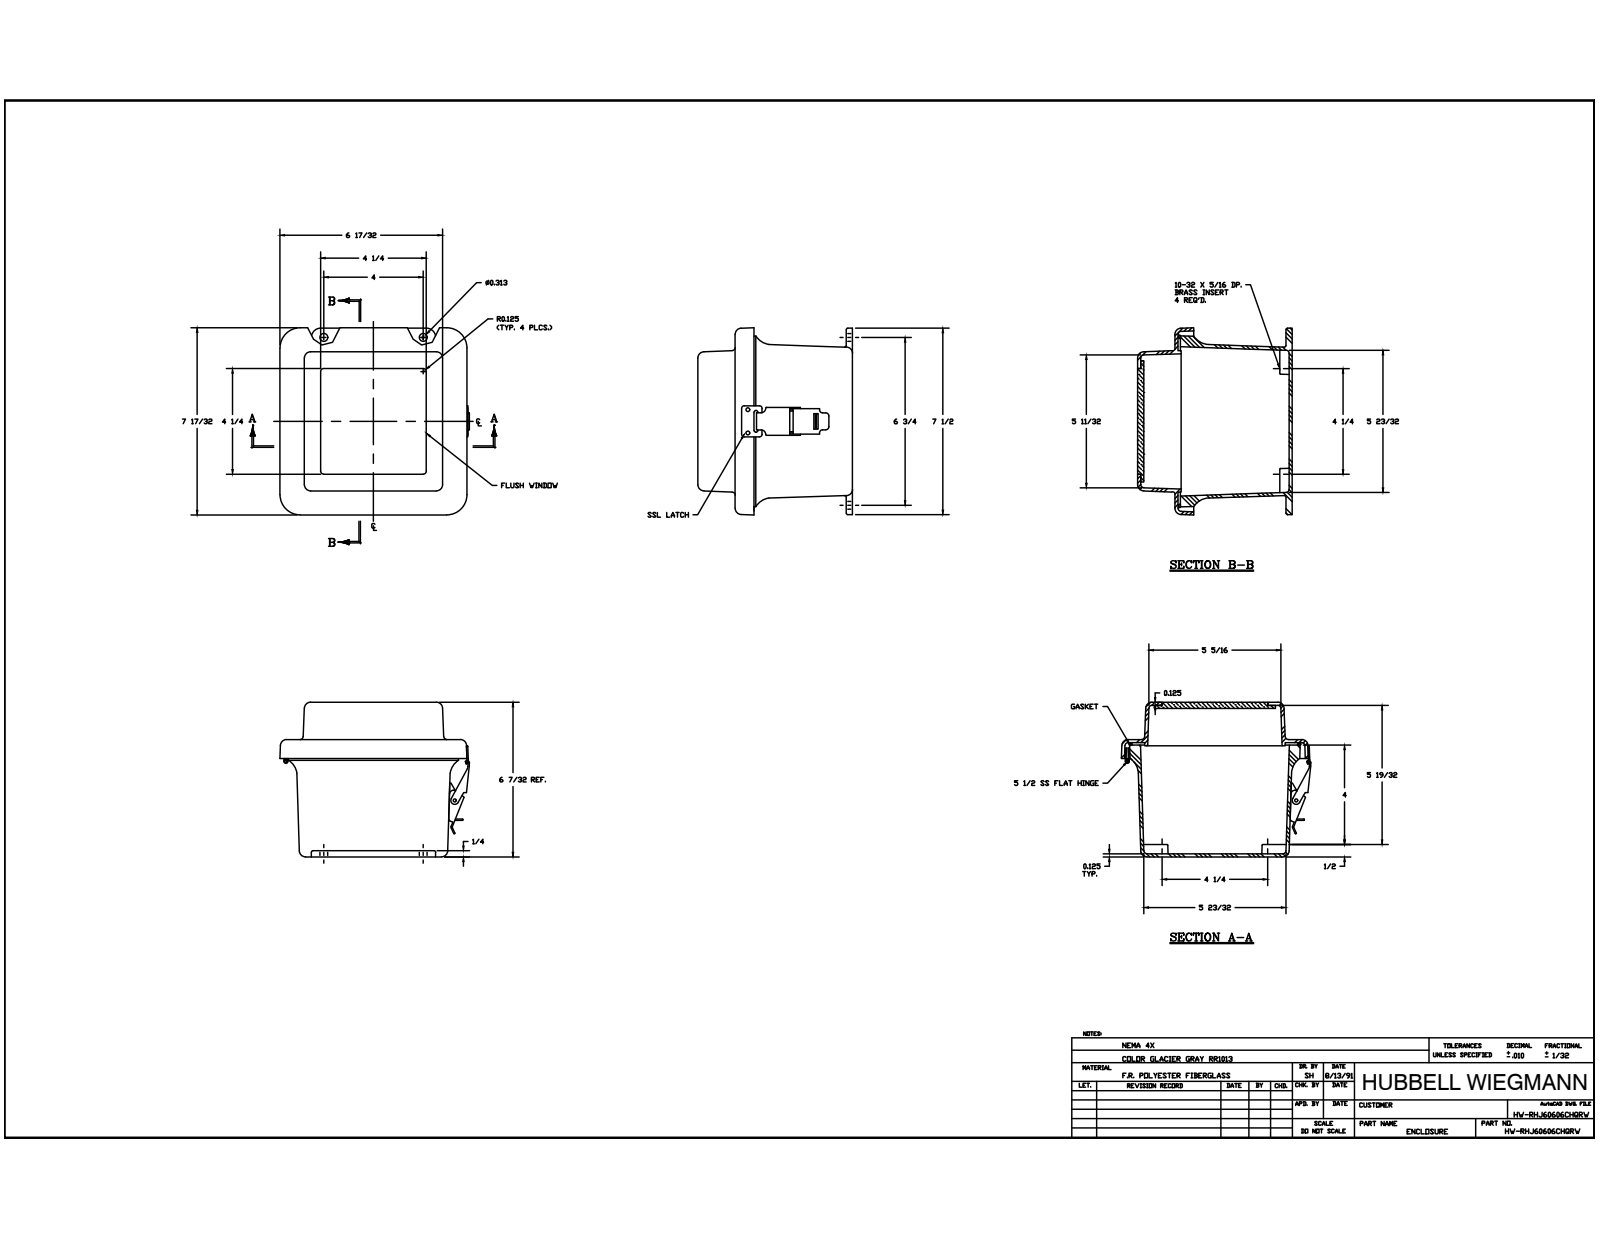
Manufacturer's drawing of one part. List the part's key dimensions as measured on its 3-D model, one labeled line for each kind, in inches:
Part name (STEP PRODUCT): J606HL_1; RMINS45821P_89; RMINS45821P_90; RMINS45821P_91 (+8 more)
STEP written by: Autodesk Inventor 2014 (AUTOMOTIVE_DESIGN)
Units: inches
Bodies: 26 solids, 725 faces (287 planar, 290 cylindrical, 148 other)
Overall size (bounding box): 7.615 × 7.525 × 6.338
Volume: 43.55 in³ · Surface area: 598.5 in²
Round holes (diameter × count): ⌀0.14 ×11, ⌀0.131 ×5, ⌀0.152 ×5, ⌀0.104 ×4, ⌀0.156 ×4, ⌀0.218 ×4, ⌀0.13 ×2, ⌀0.135 ×2, ⌀0.085 ×1, ⌀0.375 ×1
Round bosses / shafts (diameter × count): ⌀0.125 ×9, ⌀0.25 ×5, ⌀0.27 ×4, ⌀0.3 ×1, ⌀0.17 ×1, ⌀0.155 ×1, ⌀0.12 ×1
Partial cylindrical surfaces — rounded edges, fillets, slot ends (radius × count): R0.125 ×24, R0.031 ×20, R0.25 ×20, R0.015 ×12, R0.045 ×8, R0.03 ×6, R0.022 ×5, R0.06 ×4
Main face-to-face distances: 0.125, 0.125, 6.088, 0.25, 4.588, 1.5, 1.625, 6.338, 6.213, 4.713
Hole centre spacings: 5.308, 0.937, 1.37, 2.5, 4.25, 6.187, 7.38, 0.75
